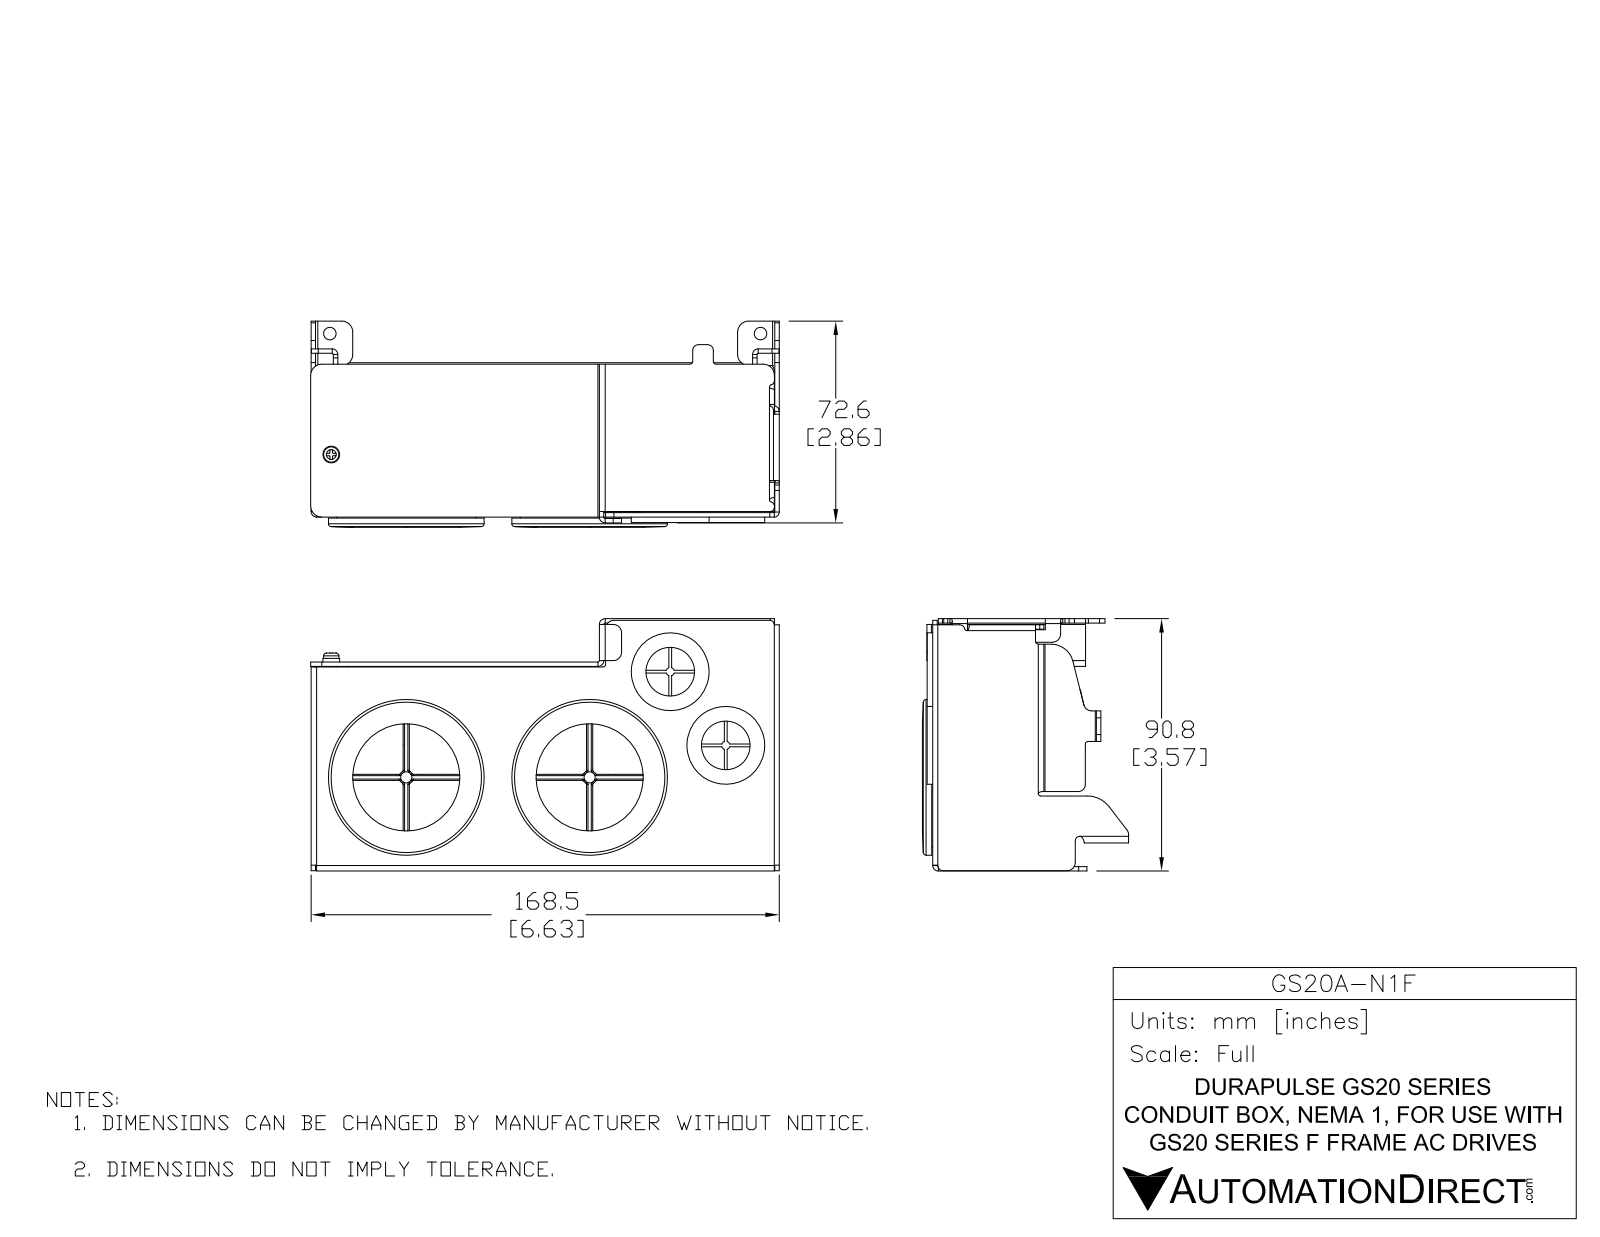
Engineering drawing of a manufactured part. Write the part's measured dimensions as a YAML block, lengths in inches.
part_name: "GS20A-N1F"
step_written_by: "SolidWorks 2017 (AUTOMOTIVE_DESIGN)"
units: inches
bodies: {solids: 8, faces: 507, planar: 189, cylindrical: 198, other: 120}
overall_size: [6.64, 3.575, 2.921]
volume: 5.272
surface_area: 158.9
round_holes:
  - {diameter: 0.157, count: 3}
  - {diameter: 0.177, count: 2}
  - {diameter: 0.689, count: 2}
  - {diameter: 0.886, count: 2}
  - {diameter: 1.516, count: 2}
  - {diameter: 1.732, count: 2}
  - {diameter: 1.972, count: 2}
  - {diameter: 0.097, count: 1}
  - {diameter: 0.138, count: 1}
round_bosses_or_shafts:
  - {diameter: 2.205, count: 2}
  - {diameter: 1.969, count: 2}
  - {diameter: 1.102, count: 2}
  - {diameter: 0.846, count: 2}
  - {diameter: 0.236, count: 1}
  - {diameter: 0.22, count: 1}
  - {diameter: 0.217, count: 1}
  - {diameter: 0.193, count: 1}
partial_cylinders:
  - {radius: 0.039, count: 22}
  - {radius: 0.079, count: 13}
  - {radius: 0.118, count: 11}
  - {radius: 0.059, count: 9}
  - {radius: 0.157, count: 9}
  - {radius: 0.016, count: 8}
  - {radius: 0.031, count: 7}
  - {radius: 0.02, count: 5}
face_to_face_distances: [0.063, 2.898, 0.614, 3.512, 6.571, 2.835, 2.961, 0.677, 6.508, 3.575]
hole_center_spacings: [1.307, 1.713, 1.882, 1.981, 2.598, 4.028, 4.55, 6.102]
